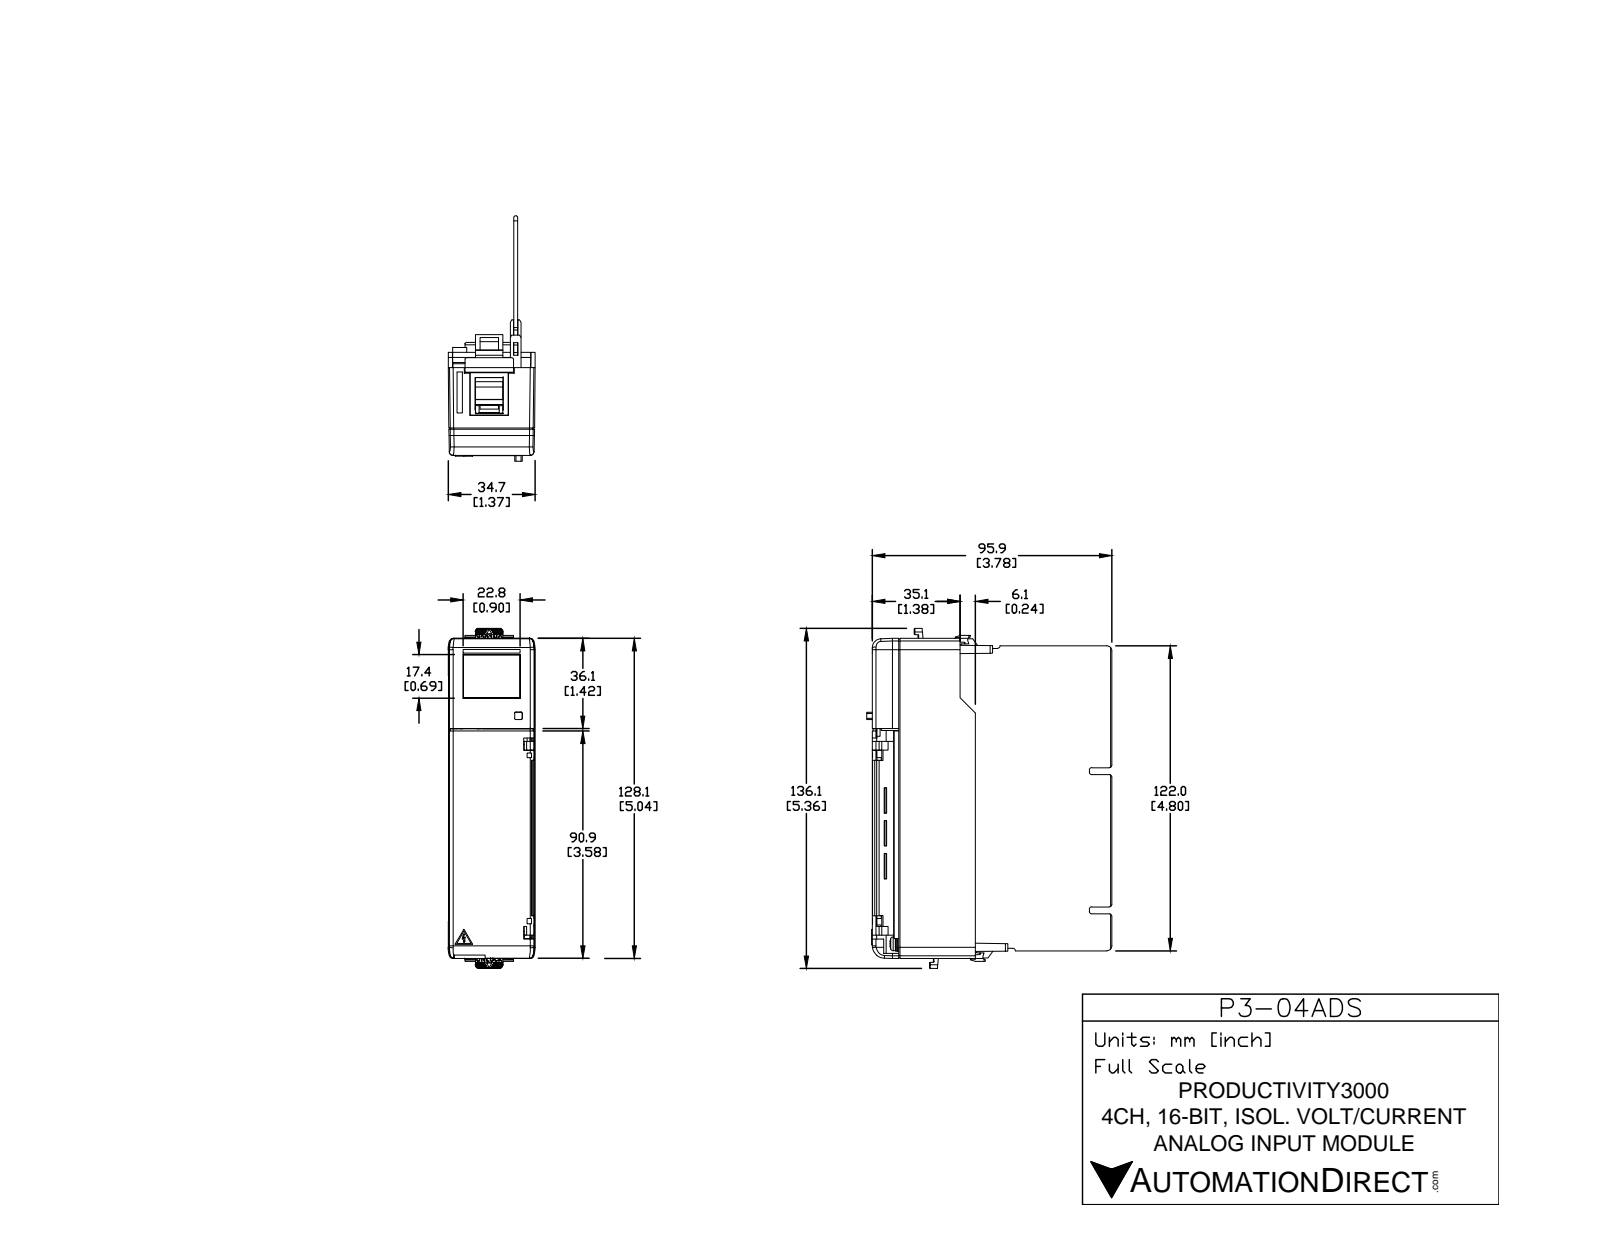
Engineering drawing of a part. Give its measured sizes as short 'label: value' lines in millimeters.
name: P3-04ADS
written by: SolidWorks 2009 (CONFIG_CONTROL_DESIGN)
unit: mm
bodies: 1 solid, 3823 faces (2833 planar, 744 cylindrical, 246 other)
size: 136.08 × 98.18 × 34.8
volume: 101 360 mm³; area: 75 361 mm²
holes: 22× ⌀3.2, 2× ⌀5, 1× ⌀1.8
bosses: 22× ⌀5.5, 22× ⌀3, 20× ⌀2.4, 2× ⌀5.6, 2× ⌀2.2, 2× ⌀2, 1× ⌀1.5
rounds: 95× R0.5, 33× R1, 29× R0.3, 22× R1.67, 13× R1.5, 6× R2, 5× R0.2, 4× R0.1
face distances: 1.6, 1.7, 28.23, 26.53, 32.56, 22.2, 2.2, 7.9, 6.8, 5.32
hole spacings: 8.68, 7.62, 13.84, 15.24, 20.59, 22.86, 27.79, 30.48
